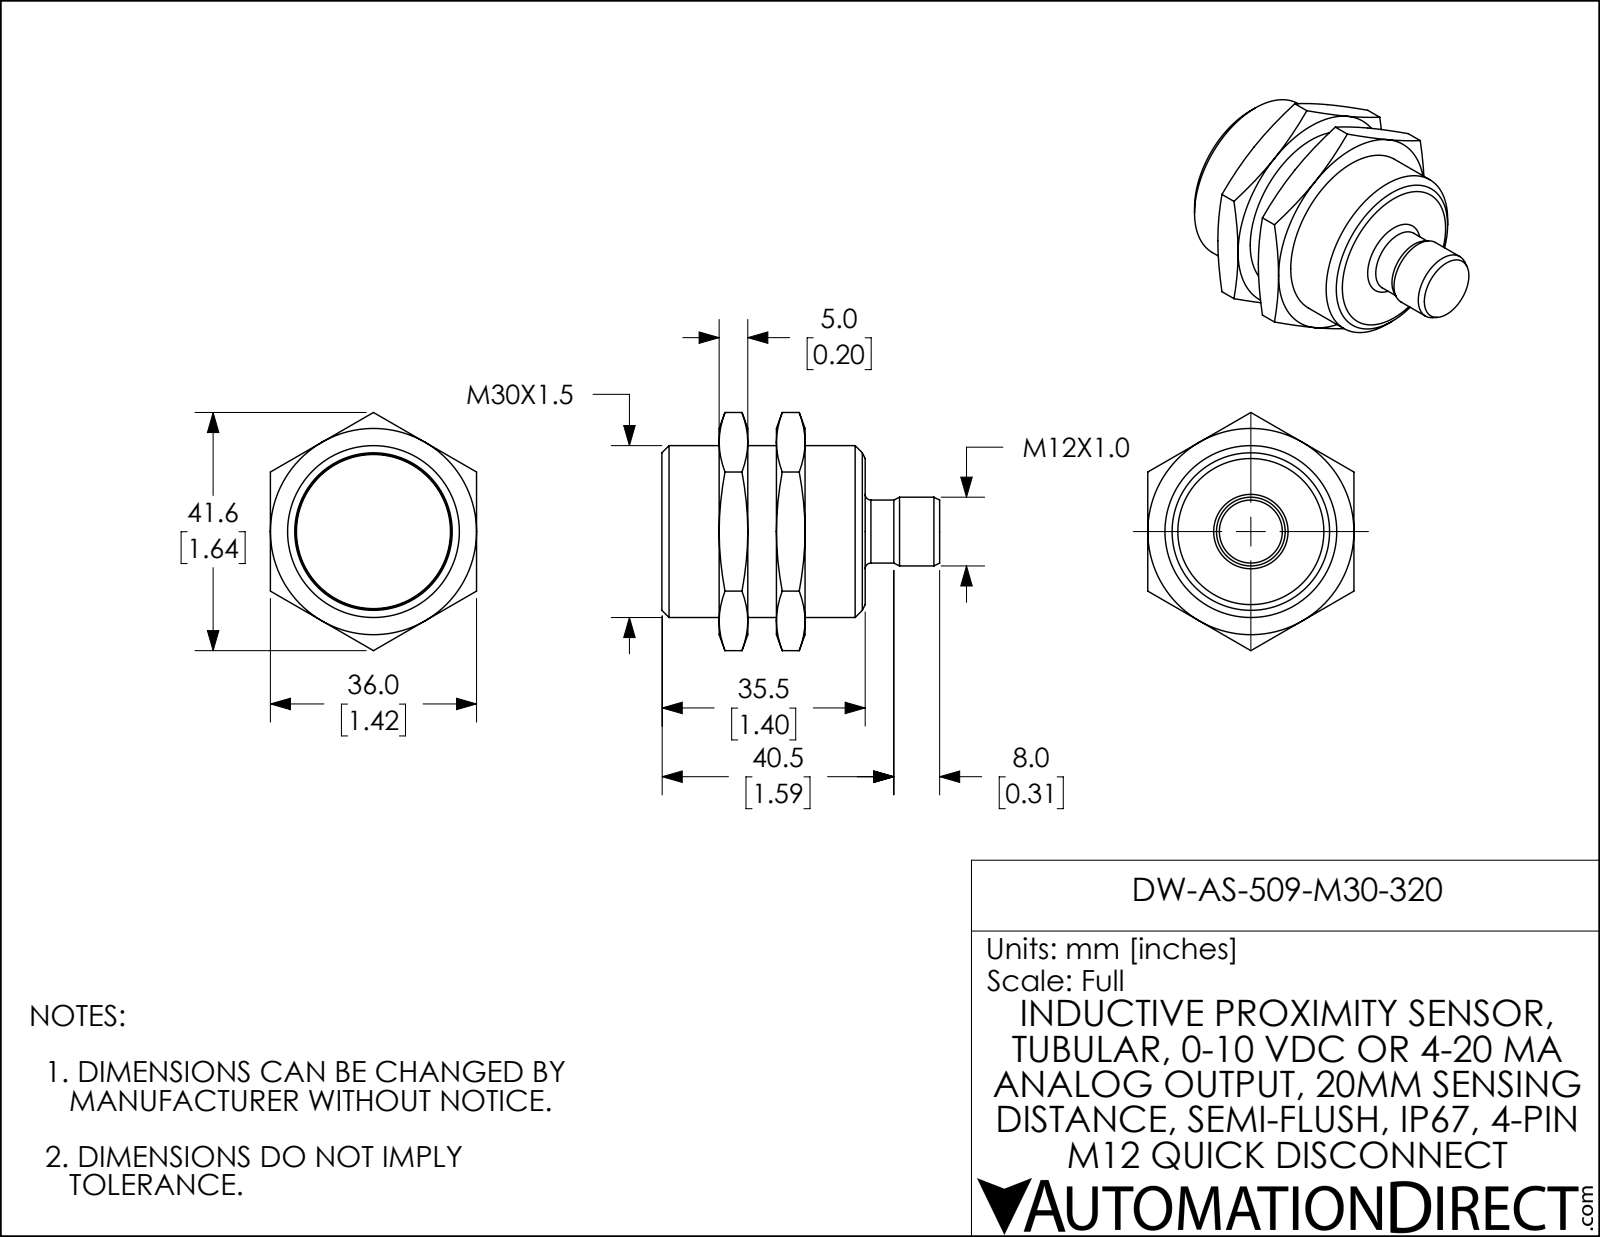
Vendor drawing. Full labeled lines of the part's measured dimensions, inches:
Part name (STEP PRODUCT): DW-AS-509-M30-320
STEP written by: SolidWorks 2018 (AUTOMOTIVE_DESIGN)
Units: inches
Bodies: 1 solid, 58 faces (21 planar, 7 cylindrical, 30 other)
Overall size (bounding box): 1.909 × 1.637 × 1.417
Volume: 1.847 in³ · Surface area: 10.65 in²
Round holes (diameter × count): ⌀1.068 ×1
Round bosses / shafts (diameter × count): ⌀1.181 ×1, ⌀1.059 ×1, ⌀0.472 ×1, ⌀0.433 ×1
Main face-to-face distances: 0.394, 0.197, 0.591, 1.417, 1.398, 0.787, 1.004, 0.61, 0.984, 0.413
